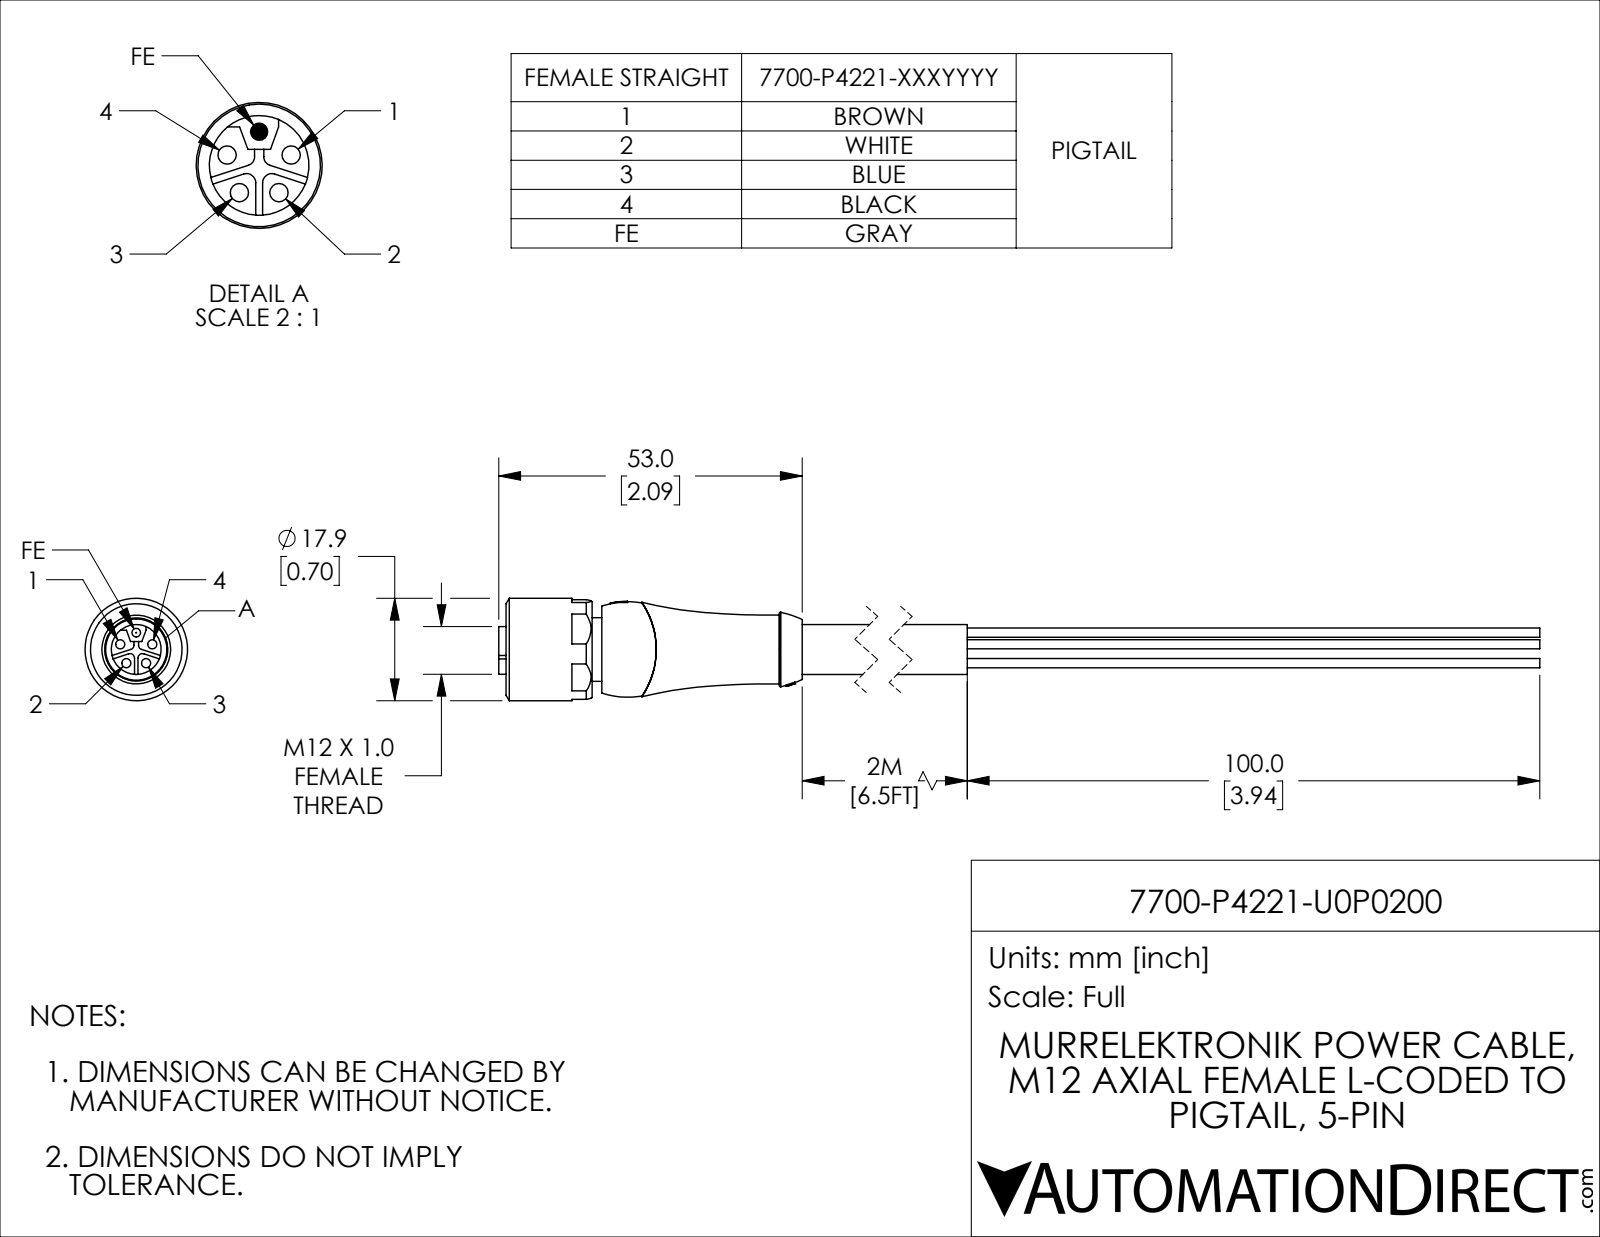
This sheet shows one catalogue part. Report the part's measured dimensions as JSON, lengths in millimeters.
{"part_name": "7700-P4221-U0P0200", "step_written_by": "SolidWorks 2021 (CONFIG_CONTROL_DESIGN)", "units": "millimeters", "bodies": {"solids": 2, "faces": 142, "planar": 69, "cylindrical": 40, "other": 33}, "overall_size": [193, 17.9, 17.9], "volume_mm3": 12000, "surface_area_mm2": 8277, "round_holes": [[1.6, 4], [11, 1], [13, 1]], "round_bosses_or_shafts": [[17.9, 1], [13, 1], [11.1, 1], [8.7, 1], [1.6, 1], [1.5, 1]], "partial_cylinders_radius": [[0.8, 4]], "face_to_face_distances": [16.7, 15, 1.7, 16.9, 91.7, 76.7, 75, 4.6, 9.2, 5.8], "hole_center_spacings": [2.9, 3.5, 5.6]}
